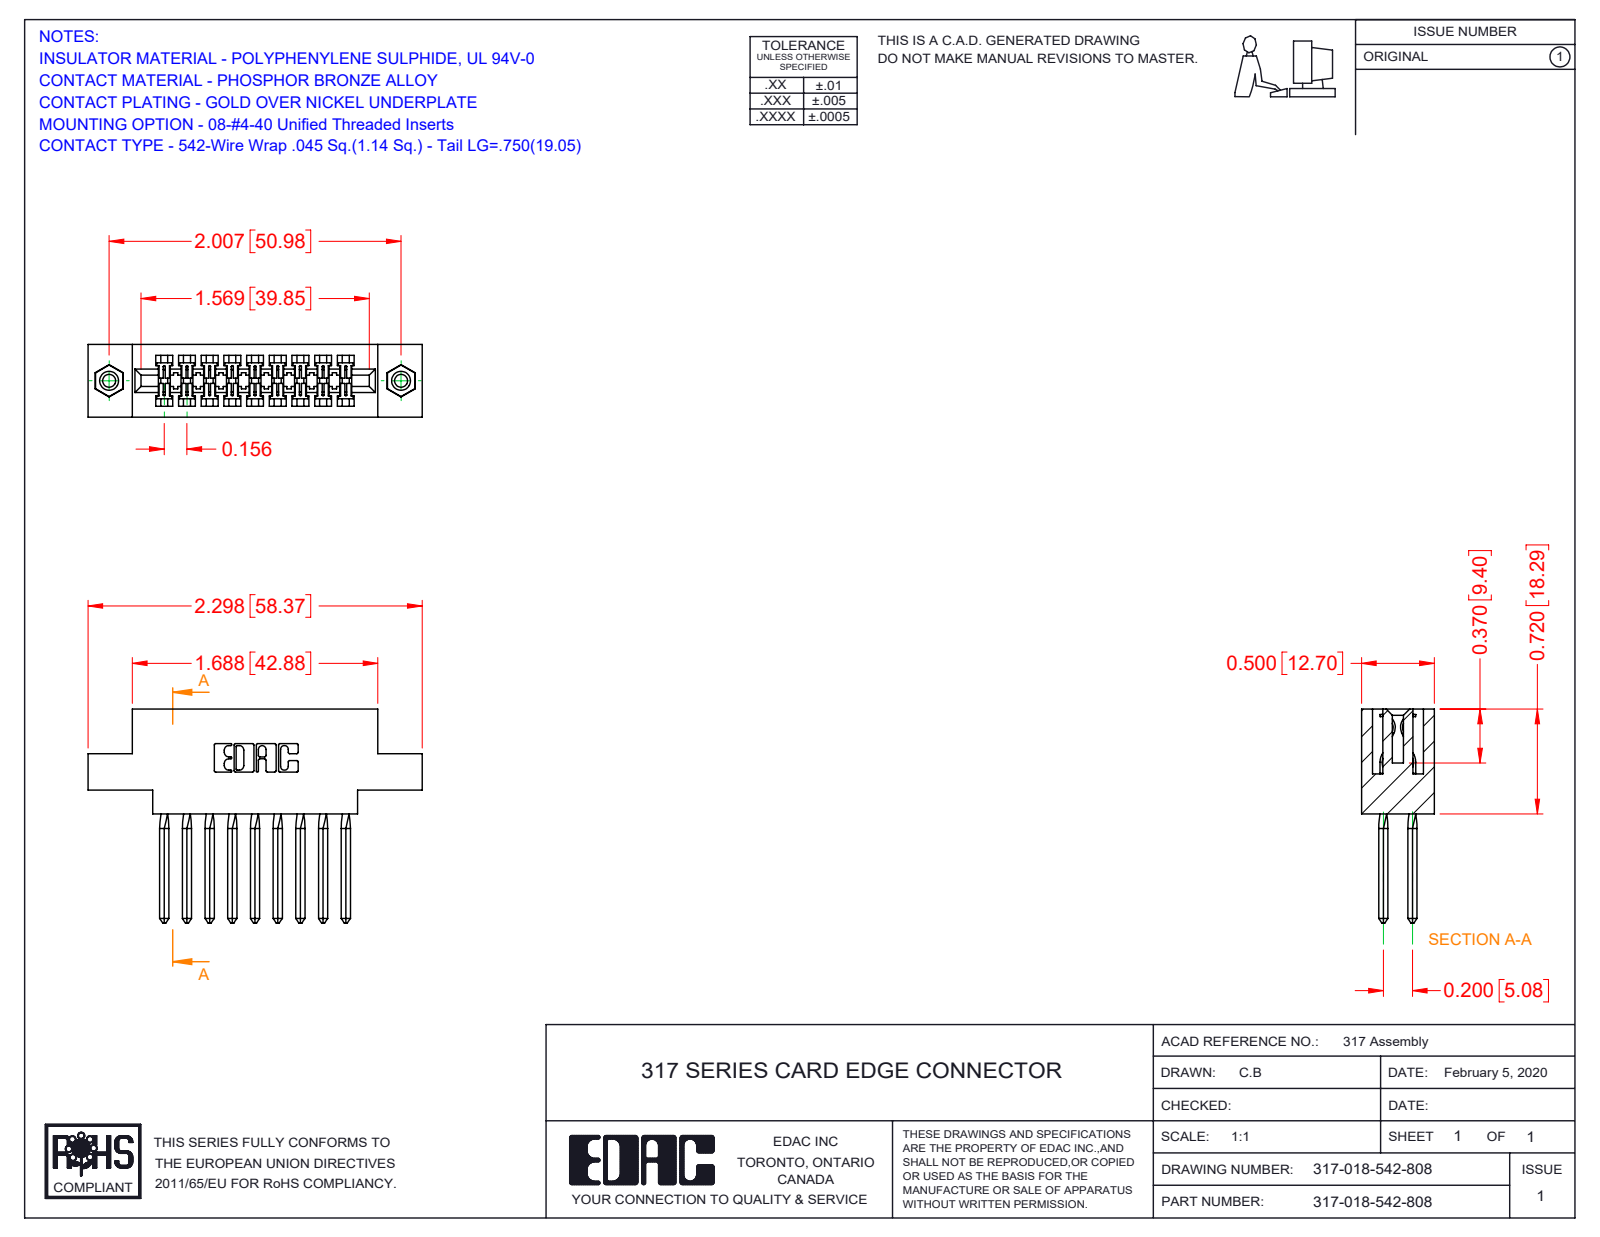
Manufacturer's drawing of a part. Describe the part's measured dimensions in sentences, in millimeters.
The part is named "317-018-542-878; 345-250-001_345-250-003-102; 317 Part_.156 Dia - TI; 317-290-003_542". Its 3-D file was written by "SolidWorks 2016 (CONFIG_CONTROL_DESIGN)". It is 21 solids with 1188 faces: 918 planar, 182 cylindrical and 88 other. Overall it measures 58.4 by 37.3 by 12.7 millimeters. Its volume is 8 500 cubic millimeters and its surface area 10 790 square millimeters. Round holes: 2 of diameter 2.3, 2 of diameter 3.2, 2 of diameter 4. Round bosses or shafts: 2 of diameter 3.9. Partial cylindrical surfaces (rounded edges, fillets, slot ends): 36 of radius 0.2, 22 of radius 0.3, 6 of radius 0.2, 6 of radius 0.8, 3 of radius 0.7, 2 of radius 1.9, 2 of radius 2.3, 2 of radius 2.5. The main face-to-face distances are 12.7, 1.9, 10.8, 2.8, 2.9, 5.6, 4, 8.9, 3.5, 5.1. The hole center spacings are 51.
